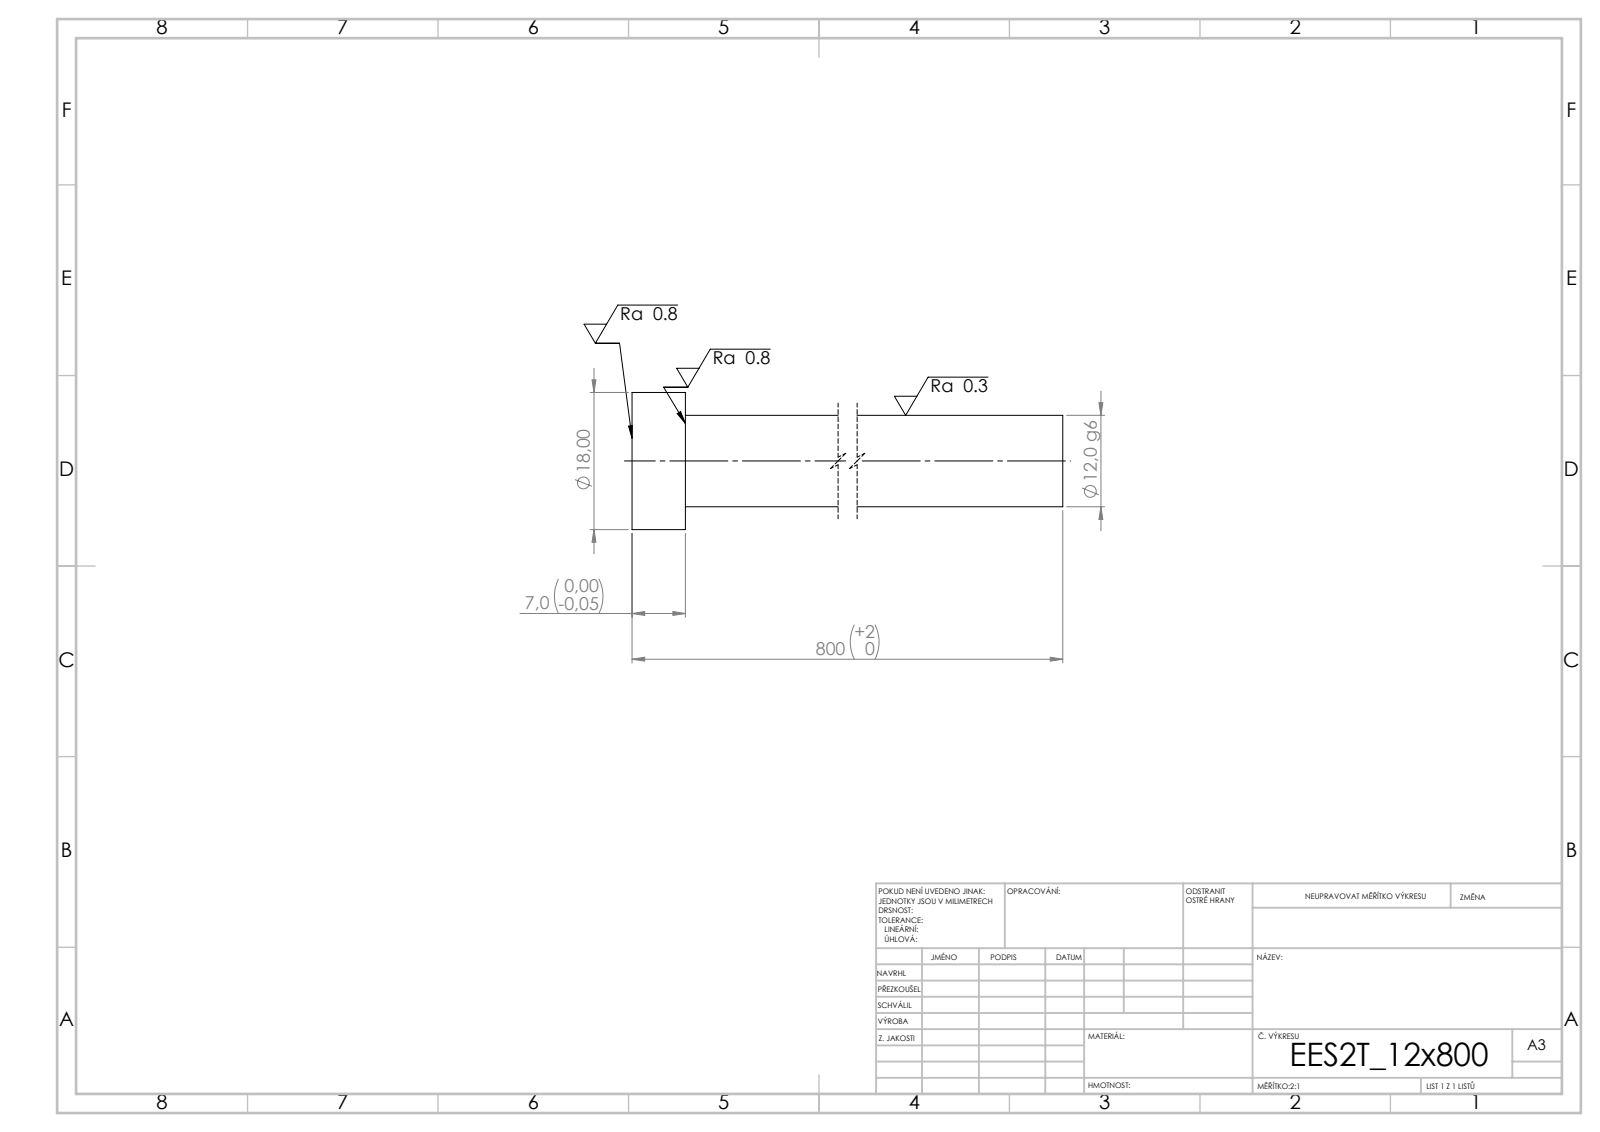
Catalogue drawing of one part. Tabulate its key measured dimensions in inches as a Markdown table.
| quantity | value |
| --- | --- |
| STEP written by | SolidWorks 2019 (CONFIG_CONTROL_DESIGN) |
| units | inches |
| bodies | 1 solid, 7 faces (3 planar, 4 cylindrical, 0 other) |
| overall size | 31.496 × 0.709 × 0.709 |
| volume | 5.582 in³ |
| surface area | 47.74 in² |
| round bosses / shafts (diameter × count) | 0.709 × 1, 0.472 × 1 |
| main face-to-face distances | 0.276, 31.496, 31.22 |
